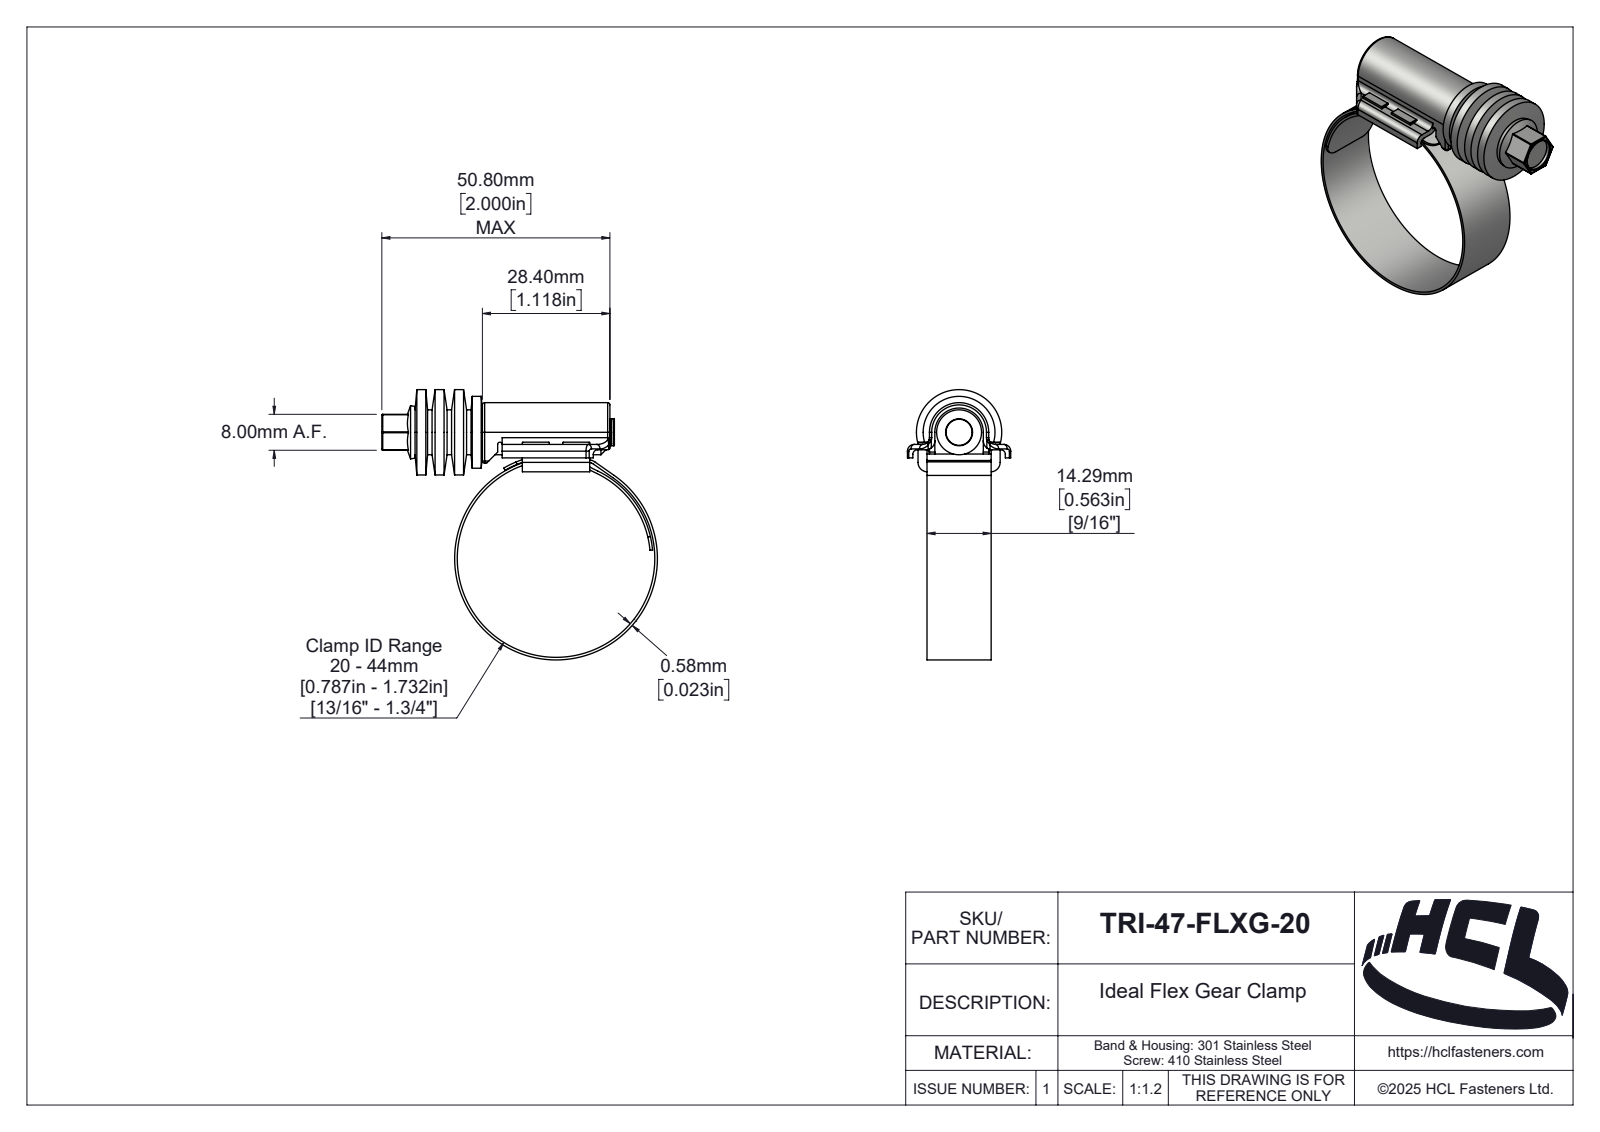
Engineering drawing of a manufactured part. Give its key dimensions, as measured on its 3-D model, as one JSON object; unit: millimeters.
{"part_name": "TRI-47-FLXG-20", "step_written_by": "SolidWorks 2025 (AUTOMOTIVE_DESIGN)", "units": "millimeters", "bodies": {"solids": 4, "faces": 322, "planar": 88, "cylindrical": 139, "other": 95}, "overall_size": [61.38, 60.18, 23], "volume_mm3": 9106, "surface_area_mm2": 11929, "round_holes": [[7, 1], [44, 1]], "round_bosses_or_shafts": [[45.16, 1], [19, 1], [16, 1], [10, 1], [6, 1], [5, 1]], "partial_cylinders_radius": [[0.2, 12], [0.5, 9], [1, 8], [1.5, 4], [3, 4], [2, 3], [0.1, 2], [2.1, 2]], "face_to_face_distances": [2, 1.2, 4.9, 1.74, 12.54, 16.29, 14.28, 6.1, 0.54, 13.74]}
